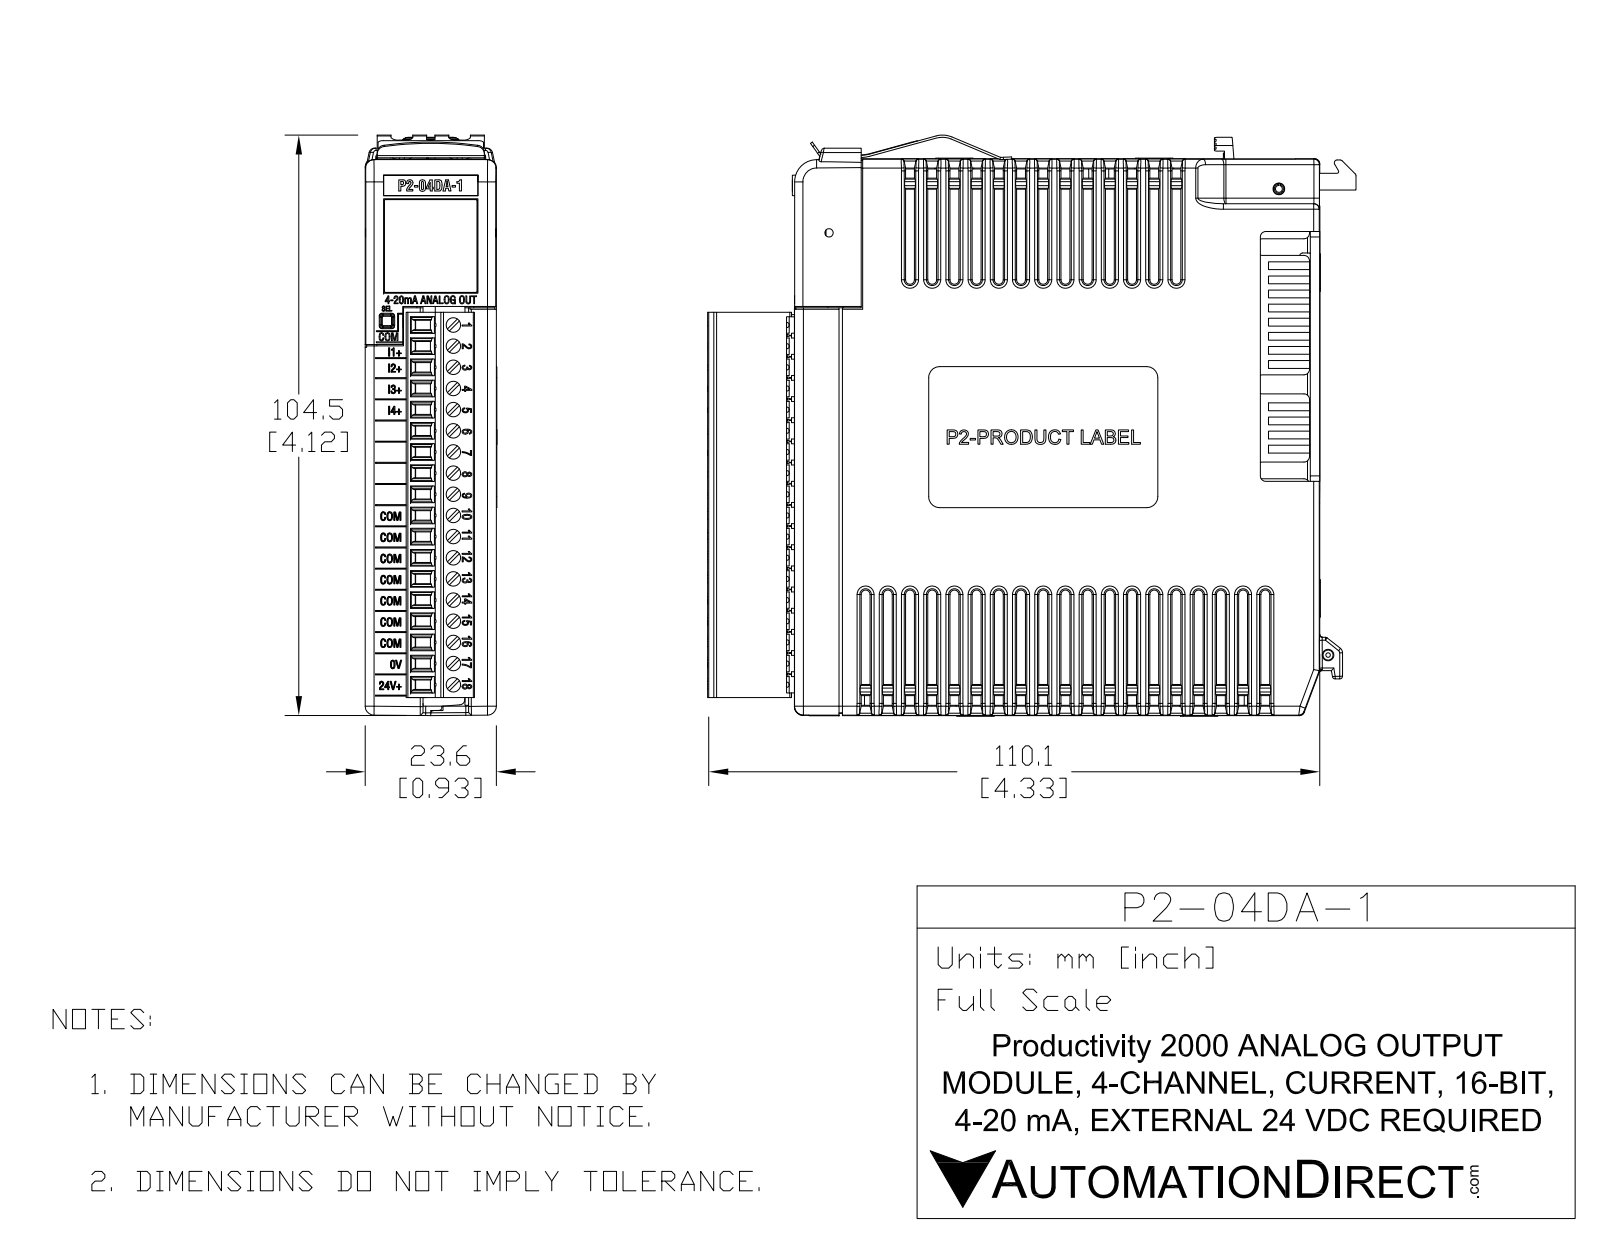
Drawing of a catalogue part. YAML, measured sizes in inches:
part_name: "P2-04DA-1 r1 Coord rred2 ext comb 1 Ext Comb fXTb"
step_written_by: "SolidWorks 2017 (AUTOMOTIVE_DESIGN)"
units: inches
bodies: {solids: 6, faces: 3396, planar: 2204, cylindrical: 564, other: 628}
overall_size: [4.12, 4.112, 0.961]
volume: 12.77
surface_area: 65.11
round_holes:
  - {diameter: 0.049, count: 3}
  - {diameter: 0.059, count: 1}
round_bosses_or_shafts:
  - {diameter: 0.016, count: 4}
  - {diameter: 0.079, count: 1}
  - {diameter: 0.028, count: 1}
partial_cylinders:
  - {radius: 0.02, count: 152}
  - {radius: 0.008, count: 116}
  - {radius: 0.039, count: 73}
  - {radius: 0.059, count: 20}
  - {radius: 0.062, count: 18}
  - {radius: 0.063, count: 13}
  - {radius: 0.012, count: 9}
  - {radius: 0.079, count: 6}
face_to_face_distances: [0.93, 0.062, 0.252, 0.707, 0.867, 0.252, 3.537, 0.016, 0.15, 0.189]
hole_center_spacings: [0.62, 3.206]
